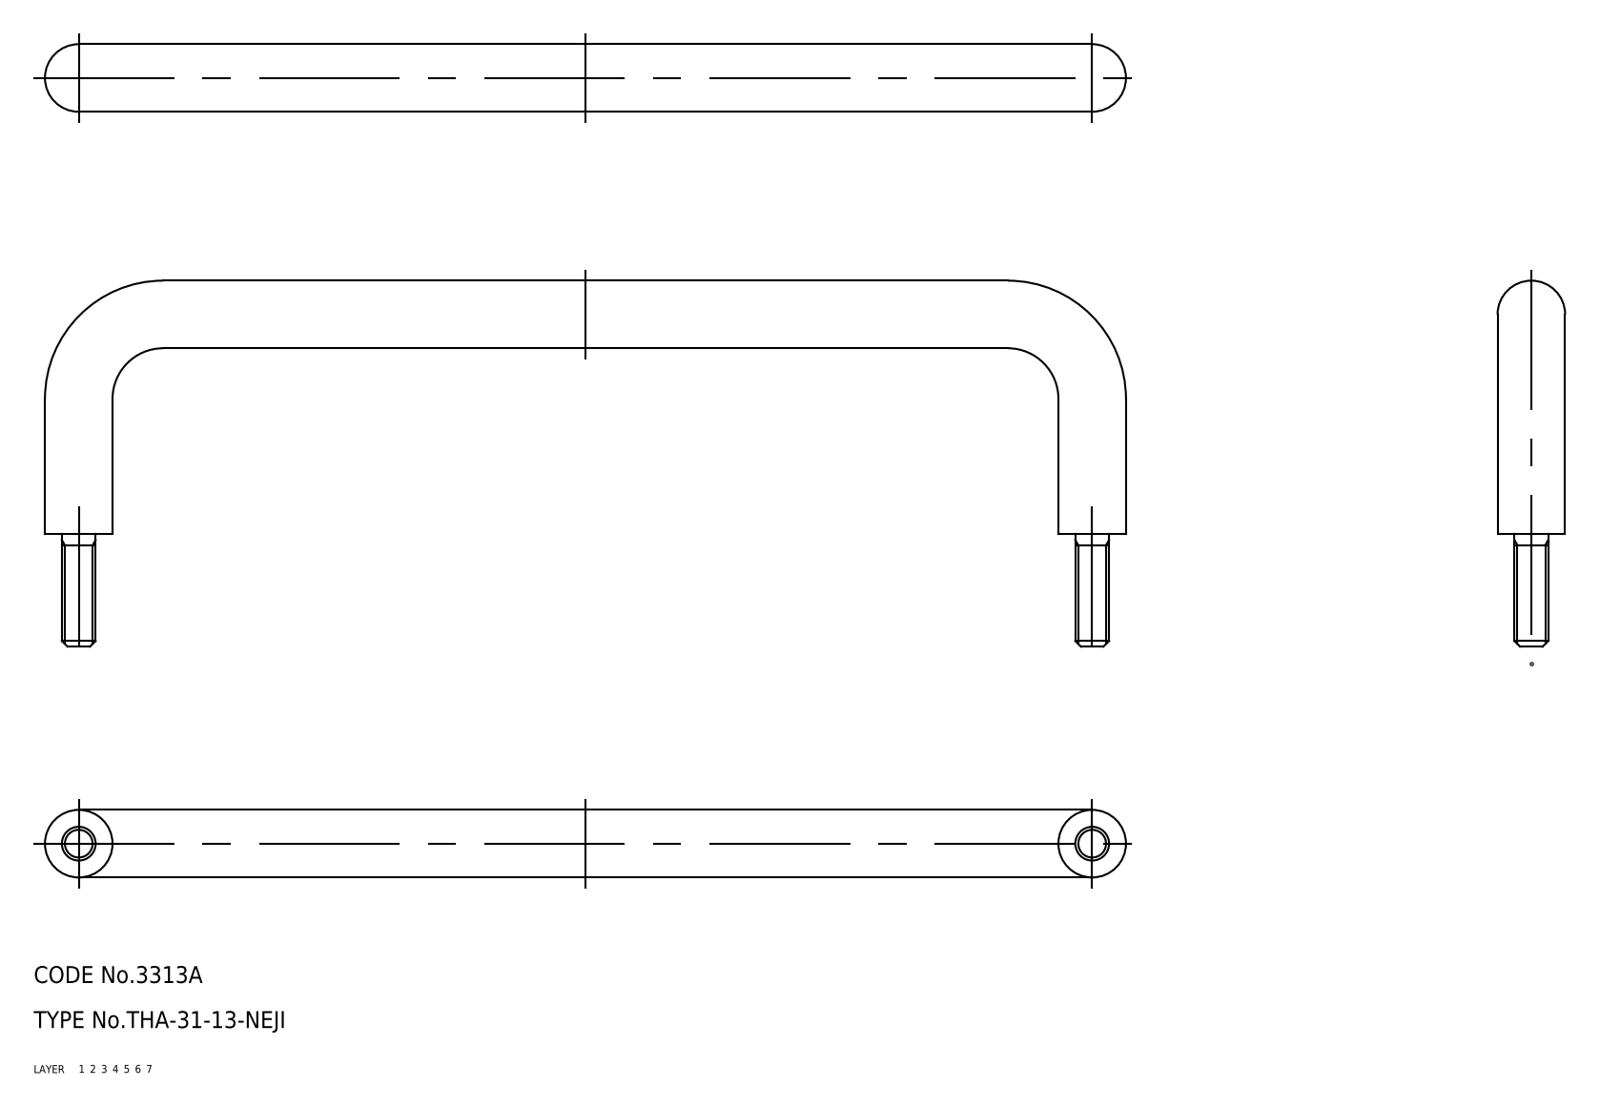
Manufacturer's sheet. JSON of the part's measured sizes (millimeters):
{"part_name": "pull", "step_written_by": "CADfix (AUTOMOTIVE_DESIGN)", "units": "millimeters", "bodies": {"solids": 1, "faces": 22, "planar": 0, "cylindrical": 0, "other": 22}, "overall_size": [192, 65, 12], "volume_mm3": 28941, "surface_area_mm2": 10202}
